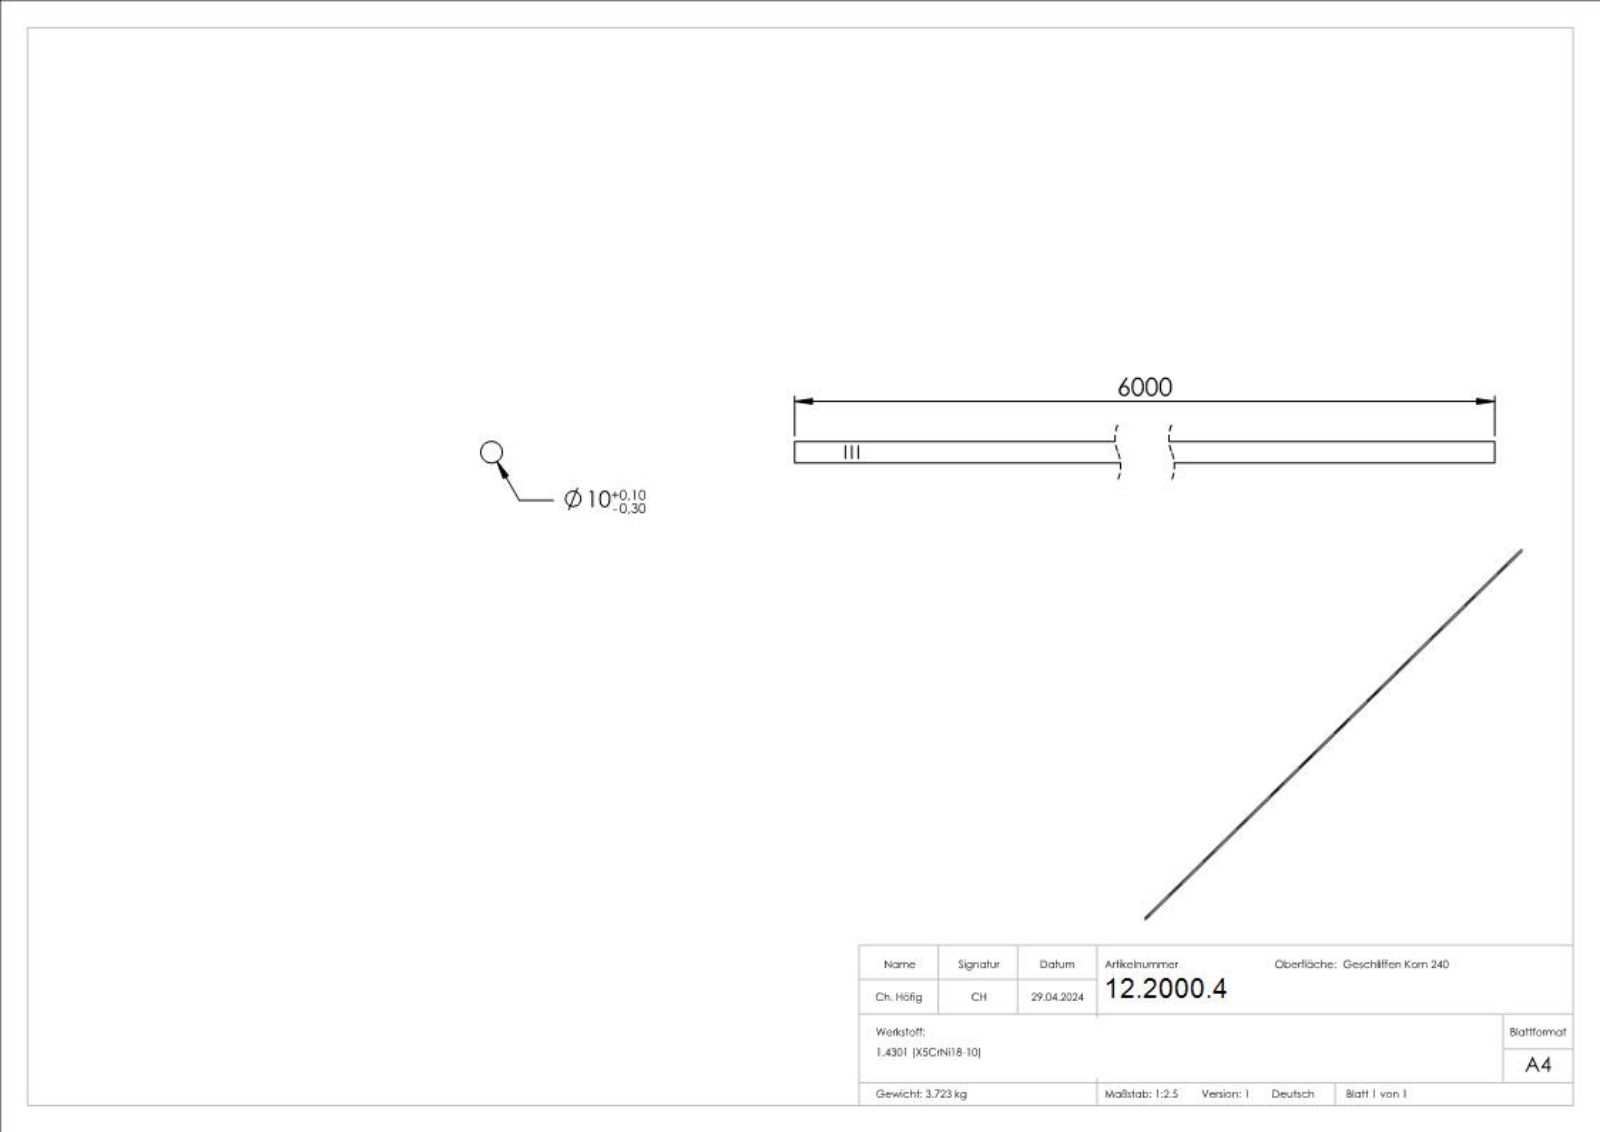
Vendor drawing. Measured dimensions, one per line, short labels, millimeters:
name: 57091-240
written by: SolidWorks 2018 (CONFIG_CONTROL_DESIGN)
unit: mm
bodies: 1 solid, 265 faces (110 planar, 32 cylindrical, 123 other)
size: 6000 × 10 × 10
volume: 471 239 mm³; area: 188 659 mm²
bosses: 1× ⌀10
rounds: 1× R4.9
face distances: 6000, 2.04, 2.41, 0.66, 0.79, 0.76, 1.13, 1.28, 3.17, 2999.84
